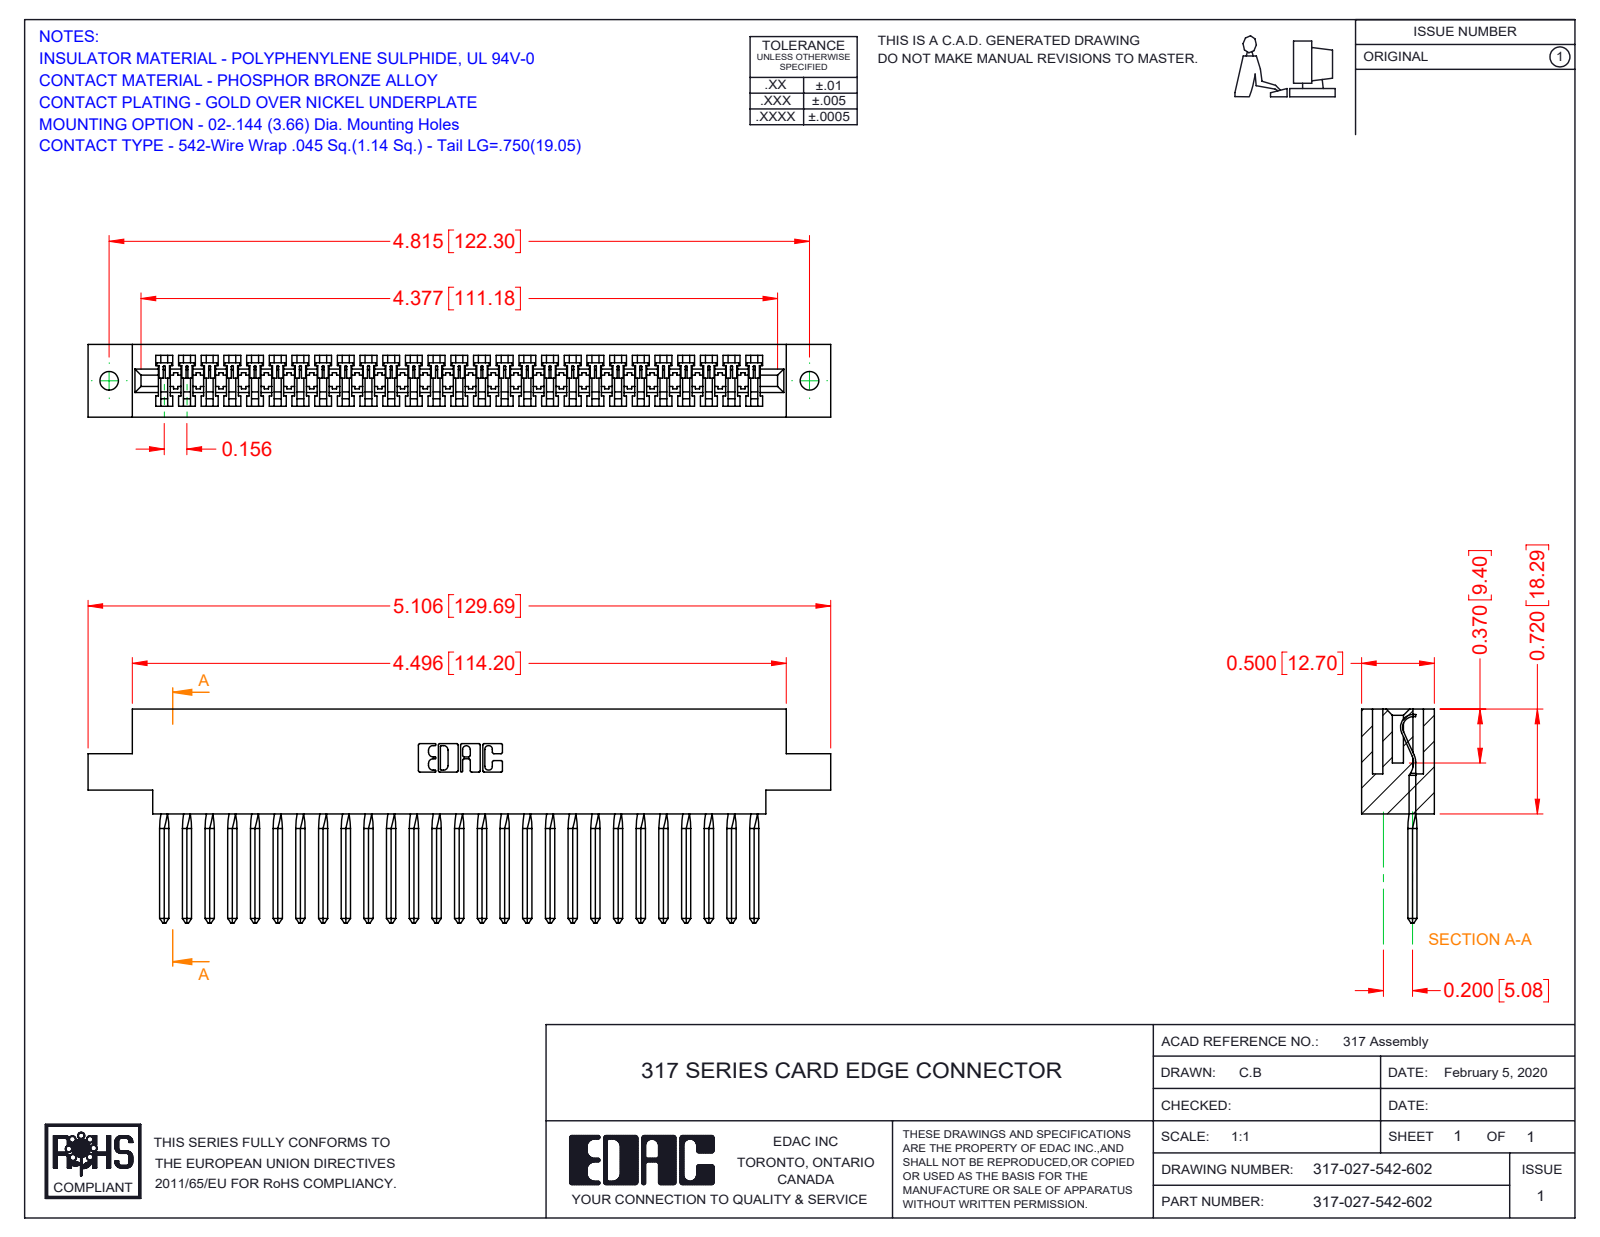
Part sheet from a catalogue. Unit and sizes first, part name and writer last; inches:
Units: inches
Overall size (bounding box): 5.106 × 1.47 × 0.5
Round holes (diameter × count): ⌀0.128 ×2
Partial cylindrical surfaces — rounded edges, fillets, slot ends (radius × count): R0.006 ×54, R0.01 ×22, R0.007 ×6, R0.031 ×6, R0.026 ×3, R0.074 ×1, R0.089 ×1, R0.1 ×1
Main face-to-face distances: 0.5, 0.075, 0.425, 0.35, 0.11, 0.72, 0.136, 0.279, 0.211, 0.289
Hole centre spacings: 4.815
Volume: 1.196 in³ · Surface area: 36.12 in²
Bodies: 28 solids, 2127 faces (1786 planar, 233 cylindrical, 108 other)
Part name (STEP PRODUCT): 317 Part_.144 Dia; 317-290-003_542; 317-027-542-602
STEP written by: SolidWorks 2016 (CONFIG_CONTROL_DESIGN)
